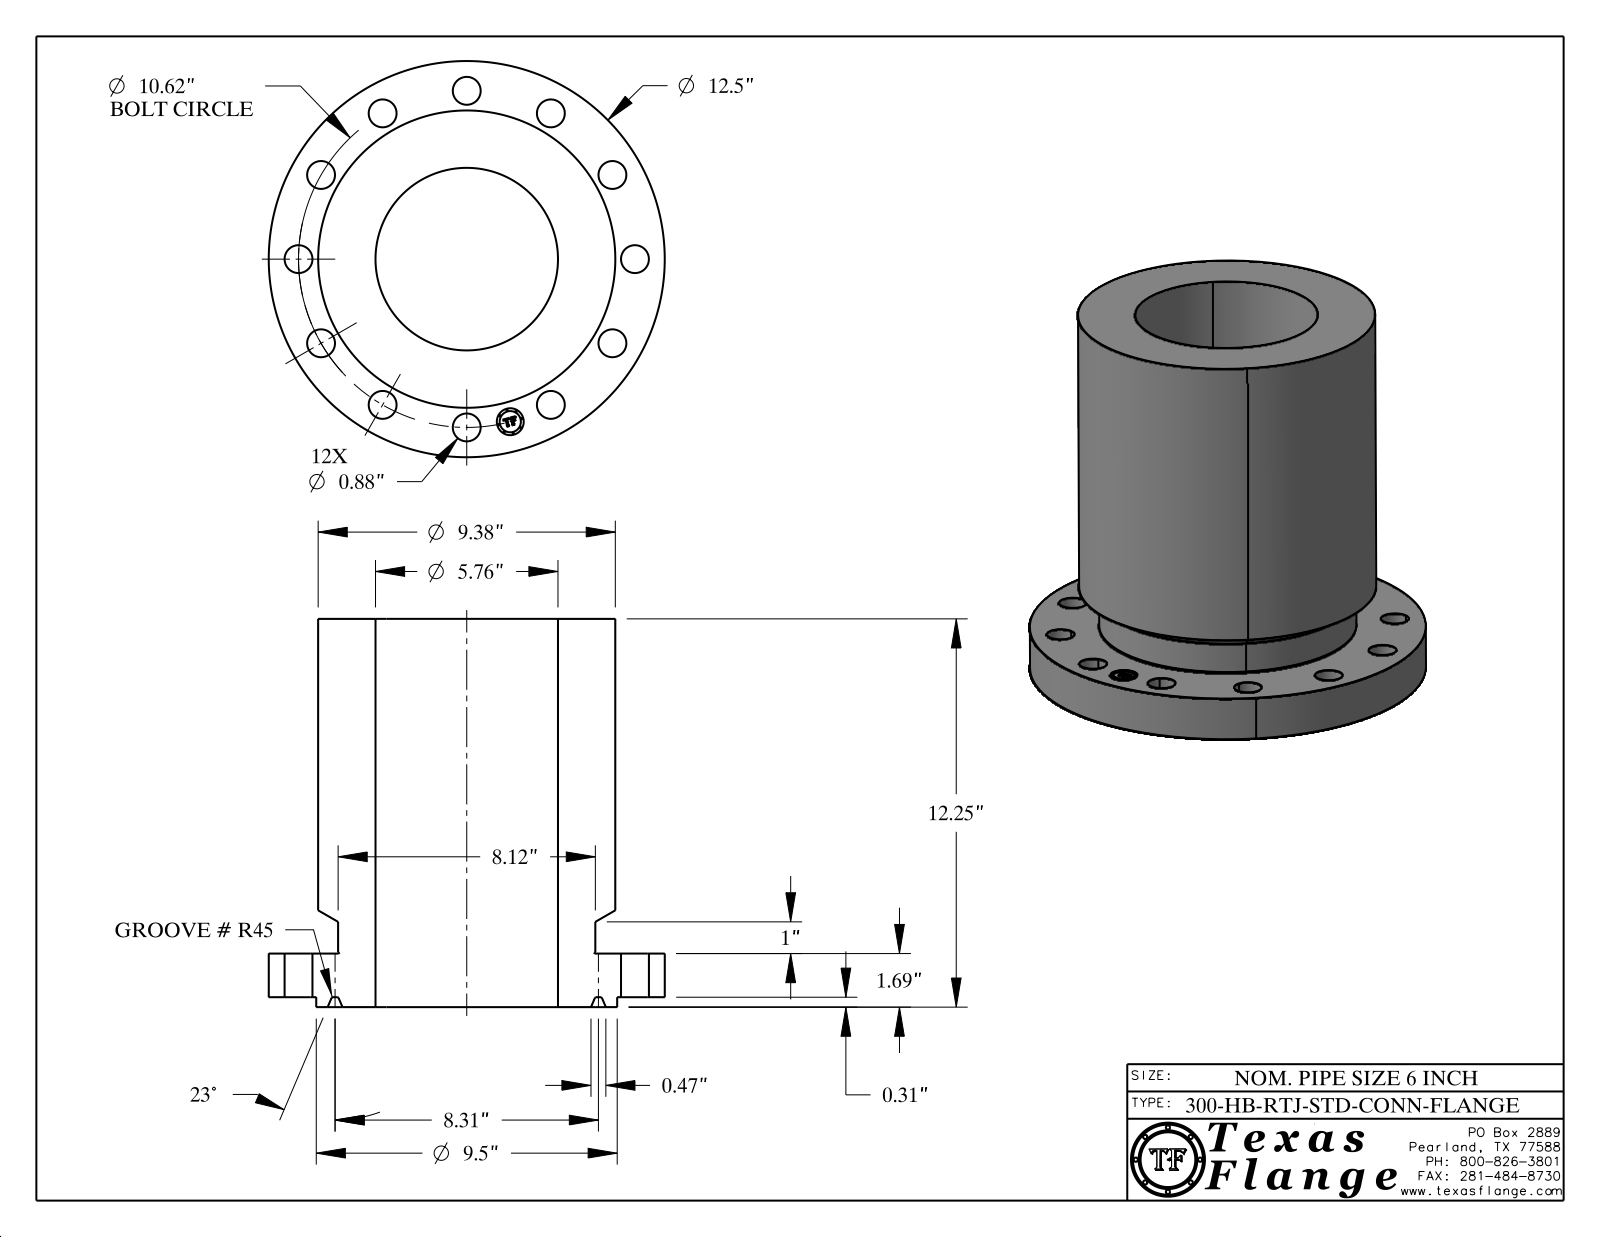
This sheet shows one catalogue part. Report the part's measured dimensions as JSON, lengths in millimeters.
{"part_name": "6-300-HB-RTJ-STD-CONN-FLANGE", "step_written_by": "CATIA V5 STEP AP214 (AUTOMOTIVE_DESIGN)", "units": "millimeters", "bodies": {"solids": 1, "faces": 439, "planar": 371, "cylindrical": 54, "other": 14}, "overall_size": [317.5, 317.5, 311.2], "volume_mm3": 9314000, "surface_area_mm2": 551600, "round_holes": [[22.4, 12], [21.6, 1], [146.3, 1]], "round_bosses_or_shafts": [[1.3, 8], [317.5, 1], [241.3, 1], [238.3, 1], [206.2, 1], [17, 1]], "face_to_face_distances": [35, 303.2, 268.2, 8, 43, 311.2, 42.8, 34.8, 268.4, 6.5], "hole_center_spacings": [134.9, 260.6, 69.8, 190.7, 233.6, 269.7, 134.9, 69.8]}
